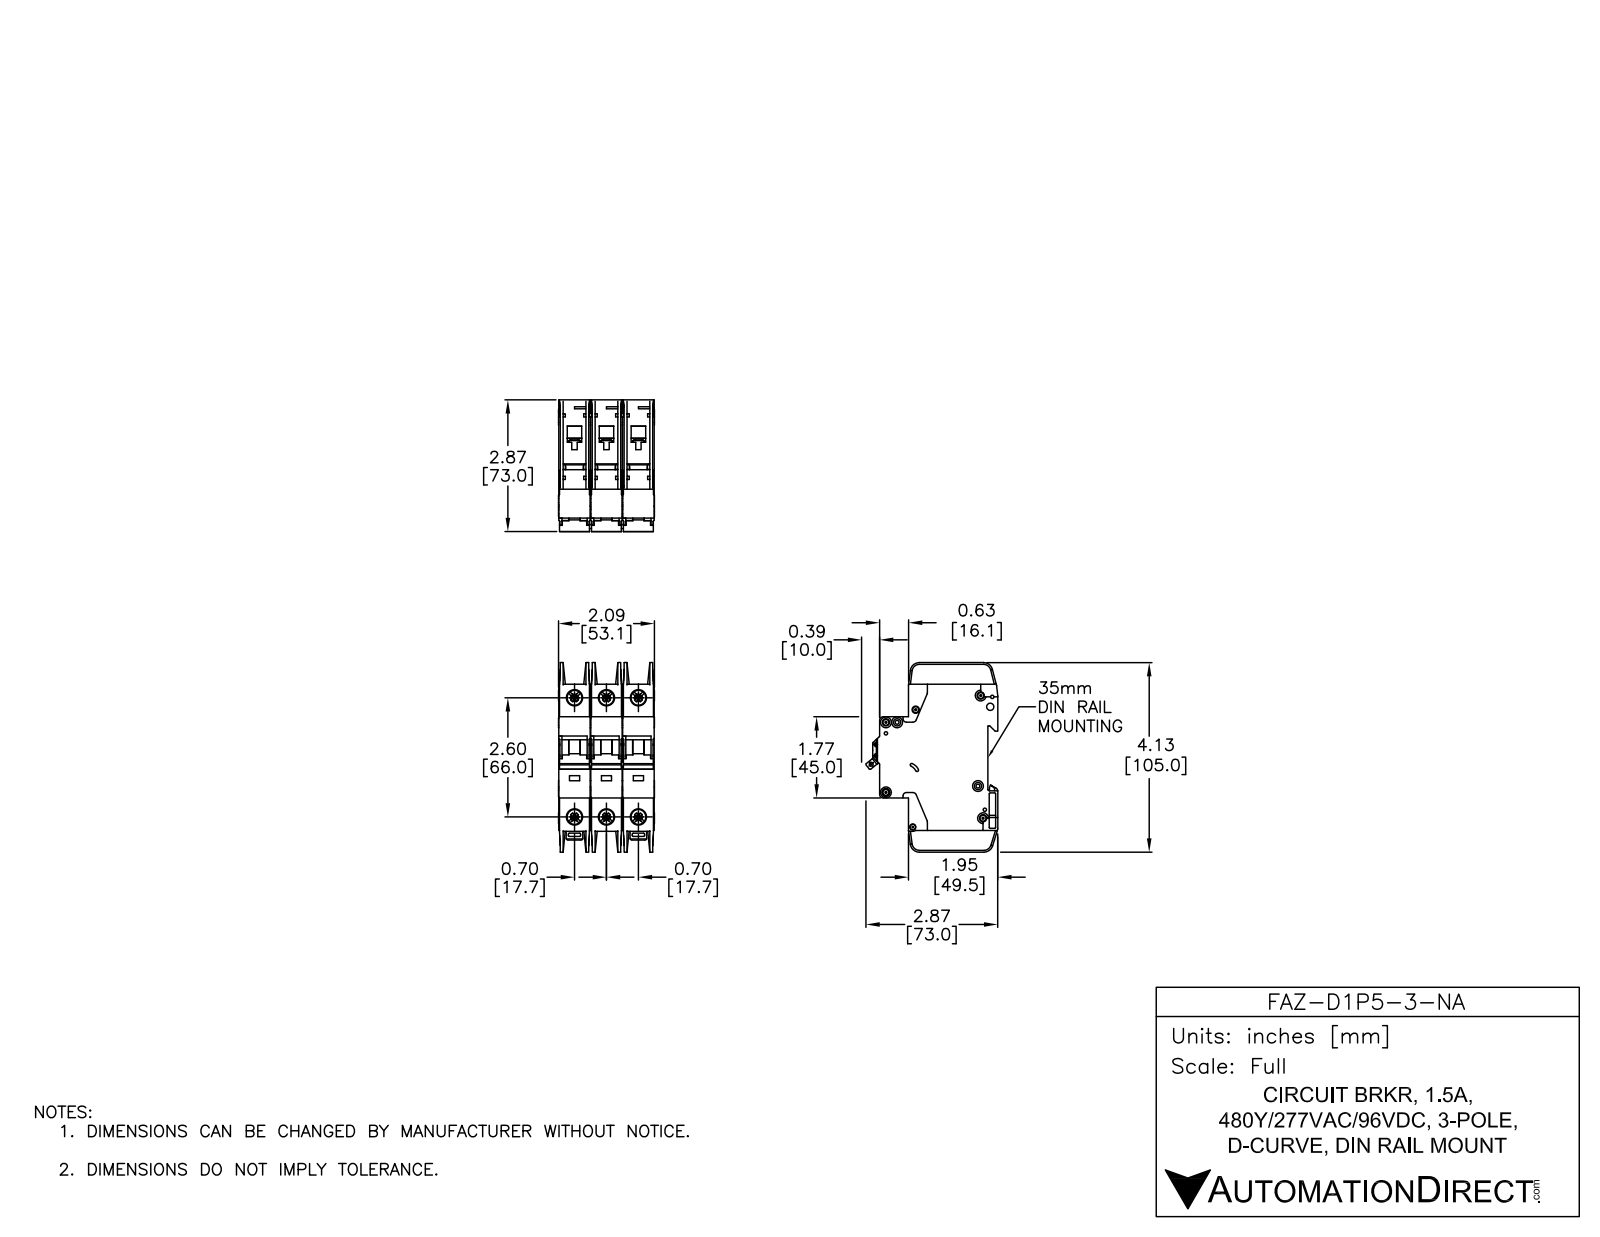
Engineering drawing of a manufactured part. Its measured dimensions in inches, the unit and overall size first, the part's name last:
Units: inches
Overall size (bounding box): 4.134 × 2.876 × 2.091
Round holes (diameter × count): ⌀0.142 ×7, ⌀0.281 ×6, ⌀0.323 ×6, ⌀0.043 ×2, ⌀0.059 ×2, ⌀0.157 ×2, ⌀0.075 ×1, ⌀0.085 ×1, ⌀0.087 ×1, ⌀0.1 ×1, ⌀0.13 ×1, ⌀0.134 ×1
Round bosses / shafts (diameter × count): ⌀0.236 ×7, ⌀0.098 ×3
Partial cylindrical surfaces — rounded edges, fillets, slot ends (radius × count): R0.01 ×65, R0.02 ×30, R0.039 ×26, R0.079 ×14, R0.071 ×5, R0.197 ×5, R0.157 ×4, R0.008 ×2
Main face-to-face distances: 0.697, 1.394, 0.689, 1.386, 0.028, 0.593, 0.096, 0.069, 0.62, 0.524
Hole centre spacings: 0.697, 2.69, 2.598, 0.244, 1.394, 2.948, 0.204, 0.24
Volume: 14.22 in³ · Surface area: 115 in²
Bodies: 9 solids, 2352 faces (1227 planar, 789 cylindrical, 336 other)
Part name (STEP PRODUCT): FAZ-D1P5-3-NA
STEP written by: SolidWorks 2014 (AUTOMOTIVE_DESIGN)
